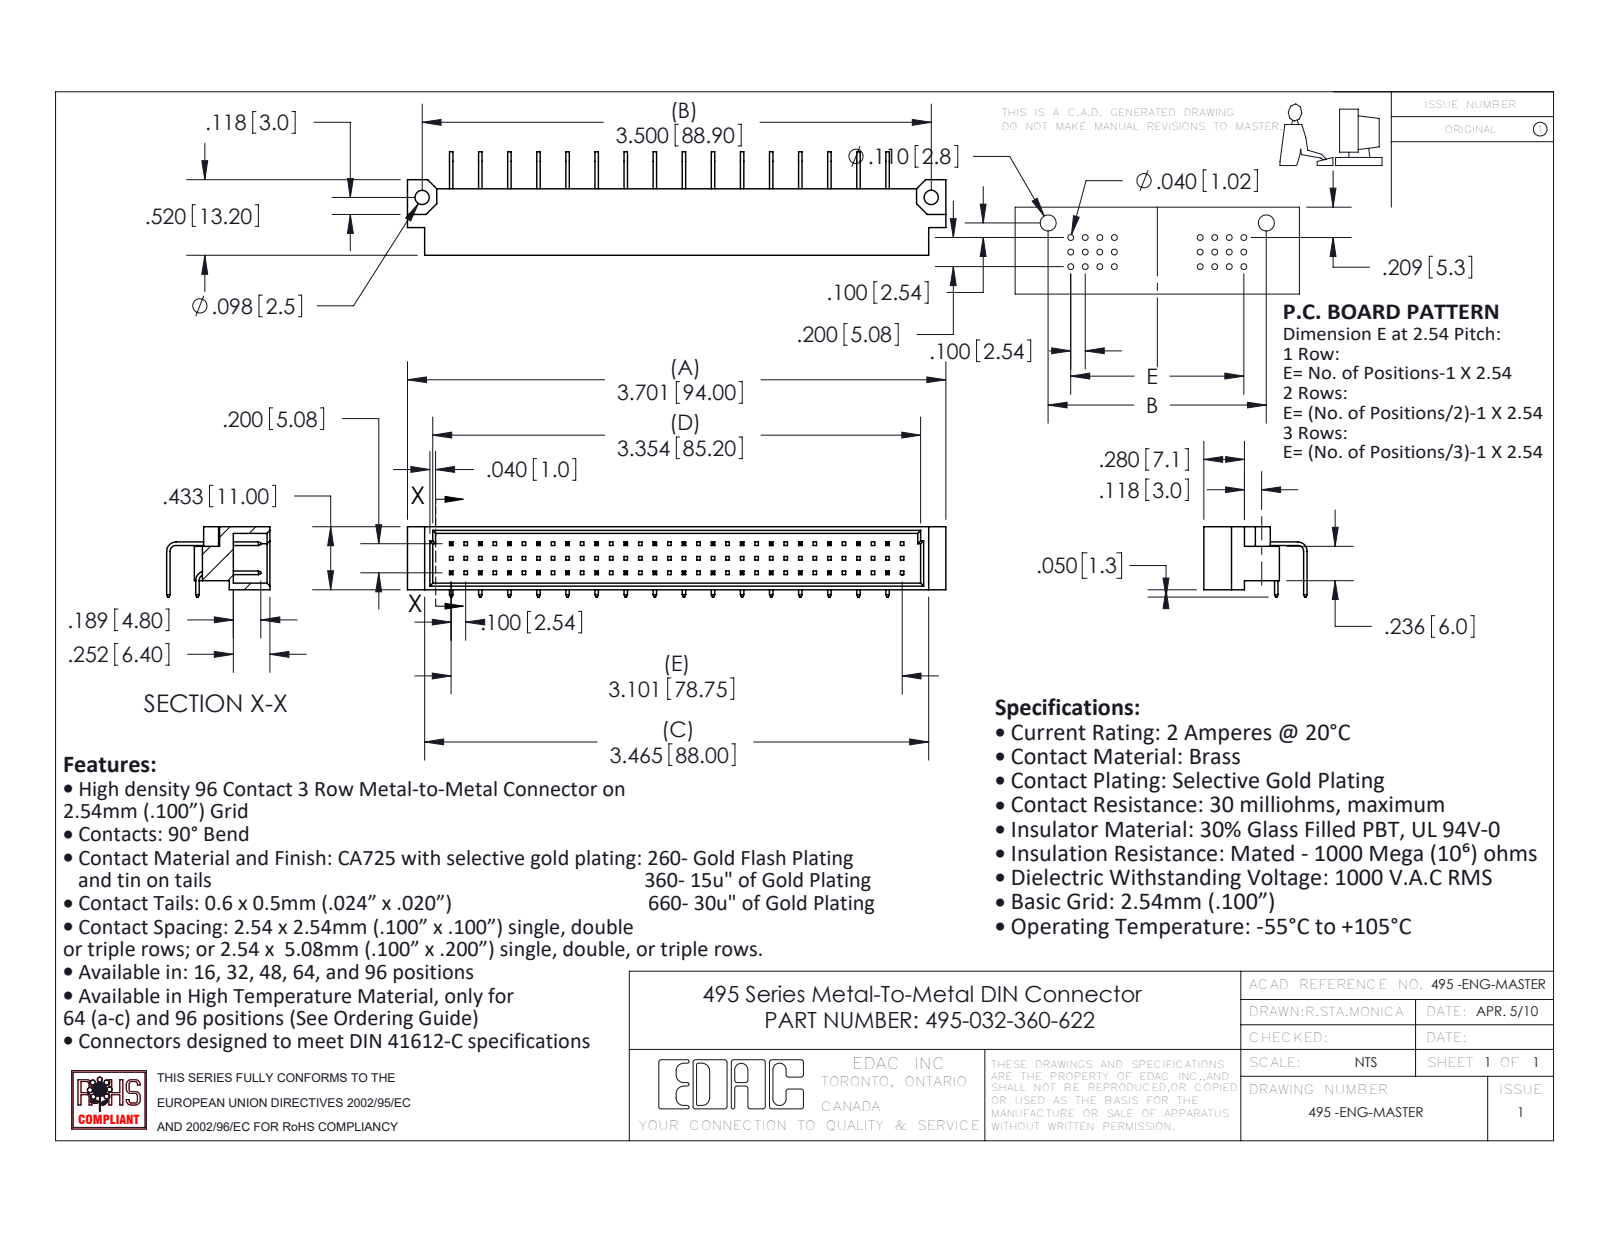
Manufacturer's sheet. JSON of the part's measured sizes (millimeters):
{"part_name": "495-290-3; 495-290-1; 495 Part_96; 495-032-360-622", "step_written_by": "SolidWorks 2020 (AUTOMOTIVE_DESIGN)", "units": "millimeters", "bodies": {"solids": 33, "faces": 1009, "planar": 941, "cylindrical": 68, "other": 0}, "overall_size": [94, 18.05, 12.27], "volume_mm3": 6161, "surface_area_mm2": 8378, "round_holes": [[2.49, 2]], "partial_cylinders_radius": [[1.02, 2], [1.65, 2]], "face_to_face_distances": [1.14, 9.86, 5.08, 5.2, 11, 0.61, 8.72, 1.6, 9.4, 0.46], "hole_center_spacings": [88.9]}
